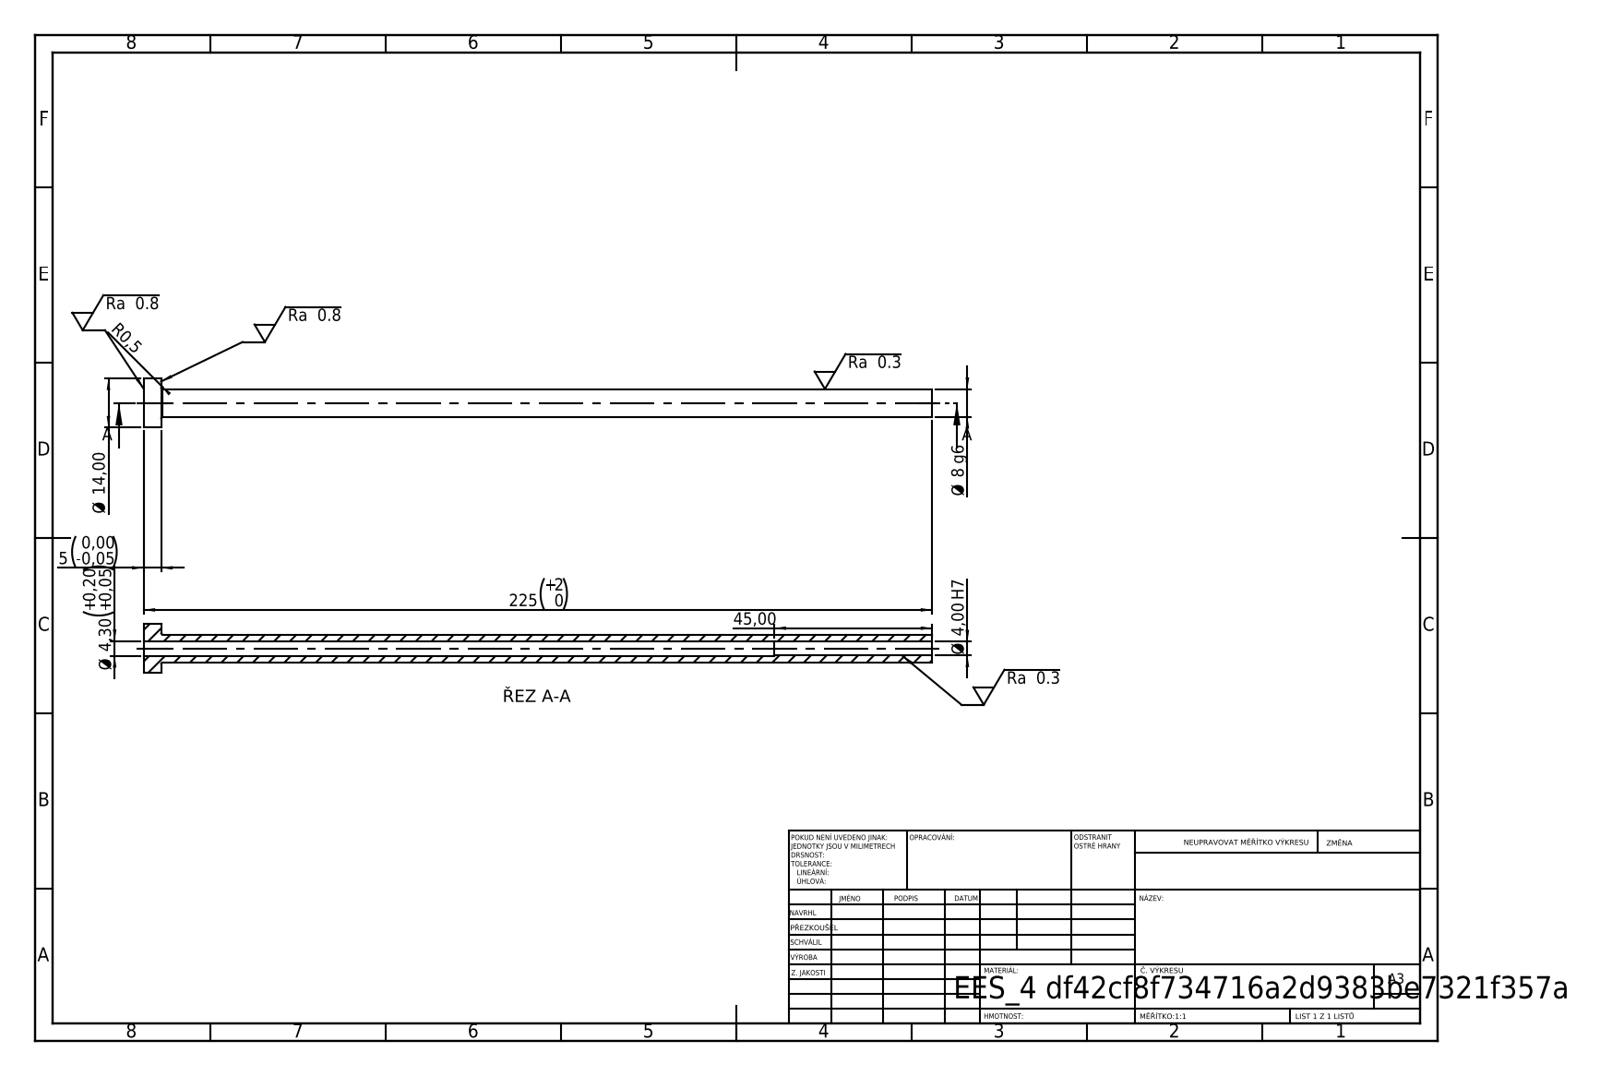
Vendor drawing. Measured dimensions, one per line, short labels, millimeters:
written by: SolidWorks 2019 (CONFIG_CONTROL_DESIGN)
unit: mm
bodies: 1 solid, 14 faces (4 planar, 8 cylindrical, 2 other)
size: 225 × 14 × 14
volume: 8 650 mm³; area: 9 024 mm²
holes: 1× ⌀4, 1× ⌀4.3
bosses: 1× ⌀14, 1× ⌀8
face distances: 5, 225, 220, 180, 175, 45
